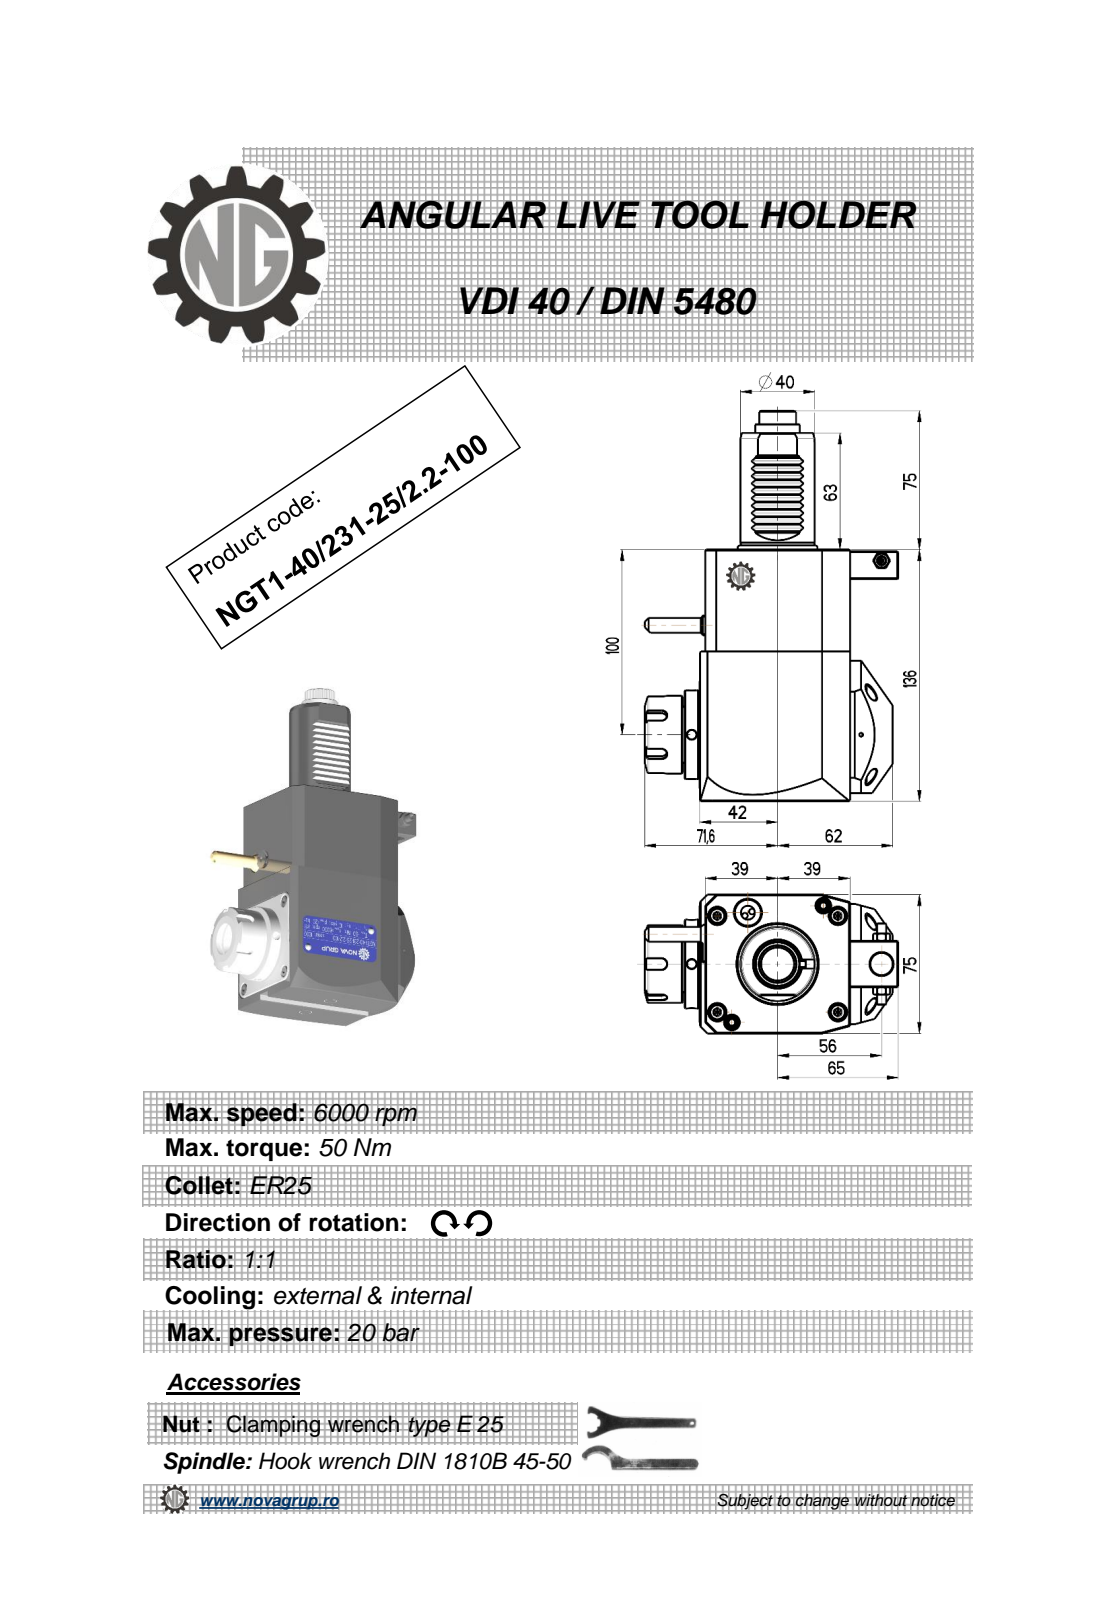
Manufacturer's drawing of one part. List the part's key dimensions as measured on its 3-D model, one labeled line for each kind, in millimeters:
Part name (STEP PRODUCT): NGT1_40_231_25_2_2_100
STEP written by: PRO/ENGINEER BY PARAMETRIC TECHNOLOGY CORPORATION, 2010280 (CONFIG_CONTROL_DESIGN)
Units: millimetres
Bodies: 1 solid, 554 faces (194 planar, 185 cylindrical, 175 other)
Overall size (bounding box): 211 × 136.6 × 76.6
Volume: 992 319 mm³ · Surface area: 76 253 mm²
Round holes (diameter × count): ⌀5 ×3, ⌀3 ×1, ⌀4.2 ×1, ⌀9.5 ×1, ⌀12 ×1, ⌀20.3 ×1
Round bosses / shafts (diameter × count): ⌀48 ×1, ⌀42 ×1, ⌀40 ×1, ⌀37.5 ×1, ⌀33 ×1, ⌀24 ×1, ⌀11.2 ×1, ⌀8.96 ×1
Partial cylindrical surfaces — rounded edges, fillets, slot ends (radius × count): R2.08 ×48, R0.26 ×12, R0.3 ×10, R0.22 ×6, R3 ×5, R9.08 ×1, R9.92 ×1, R15 ×1
Main face-to-face distances: 75, 136, 78, 81, 3, 2.8, 80.8, 7.5, 0.5, 11
Hole centre spacings: 36.22, 61.13, 91.5, 102.25, 138.89
